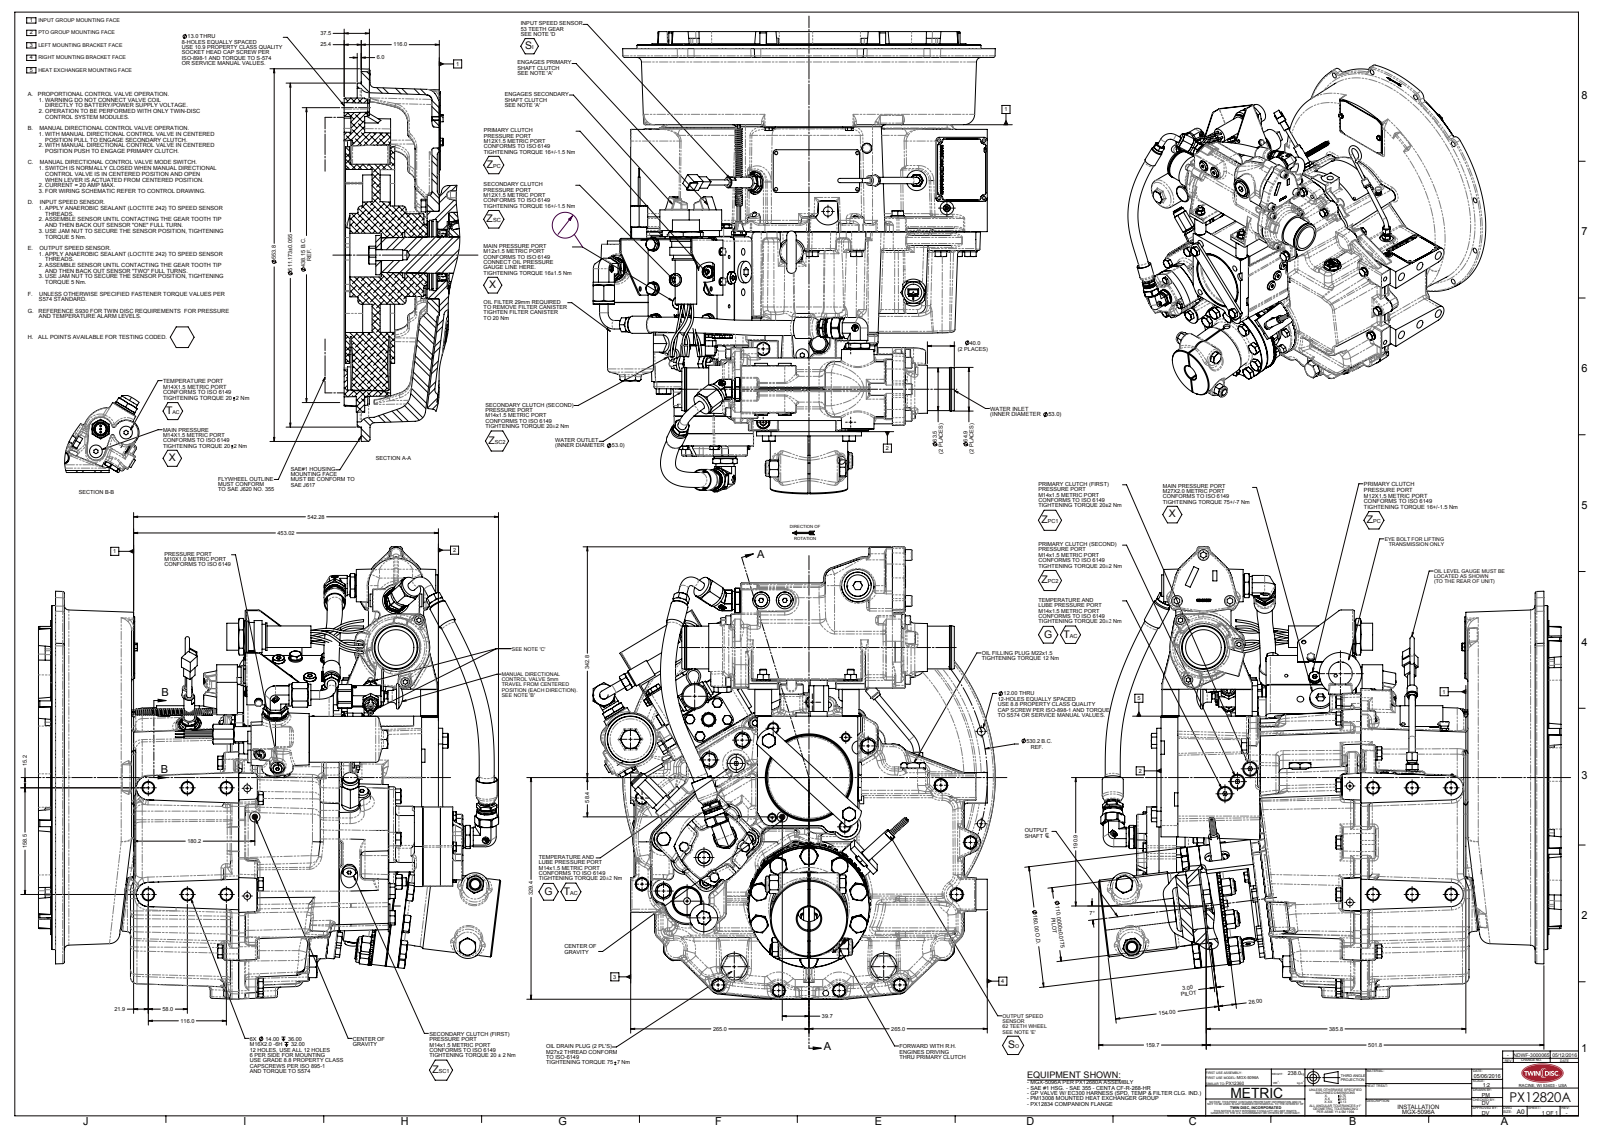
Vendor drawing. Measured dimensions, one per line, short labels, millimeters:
name: PX12820A
written by: SolidWorks 2010 (AUTOMOTIVE_DESIGN)
unit: mm
bodies: 0 solids, 6954 faces (1986 planar, 2015 cylindrical, 2953 other)
size: 686.92 × 672.6 × 597.66
holes: 12× ⌀12, 9× ⌀8.5, 6× ⌀18.82, 5× ⌀10.2, 5× ⌀18.29, 5× ⌀30, 4× ⌀4.8, 4× ⌀25, 3× ⌀40, 2× ⌀10, 2× ⌀12.8, 2× ⌀15
bosses: 23× ⌀24, 23× ⌀19.85, 11× ⌀18.9, 11× ⌀16, 7× ⌀10, 6× ⌀31.8, 6× ⌀20, 6× ⌀13
rounds: 151× R3, 137× R5, 105× R4, 85× R2.5, 76× R1, 71× R32, 67× R2, 26× R1.02
face distances: 0.5, 149.64, 159.38, 158.88, 309.02, 150.14, 308.52, 149.14, 2, 3
hole spacings: 137.23, 58, 73.35, 168.78, 265.1, 459.17, 77.76, 158.5
